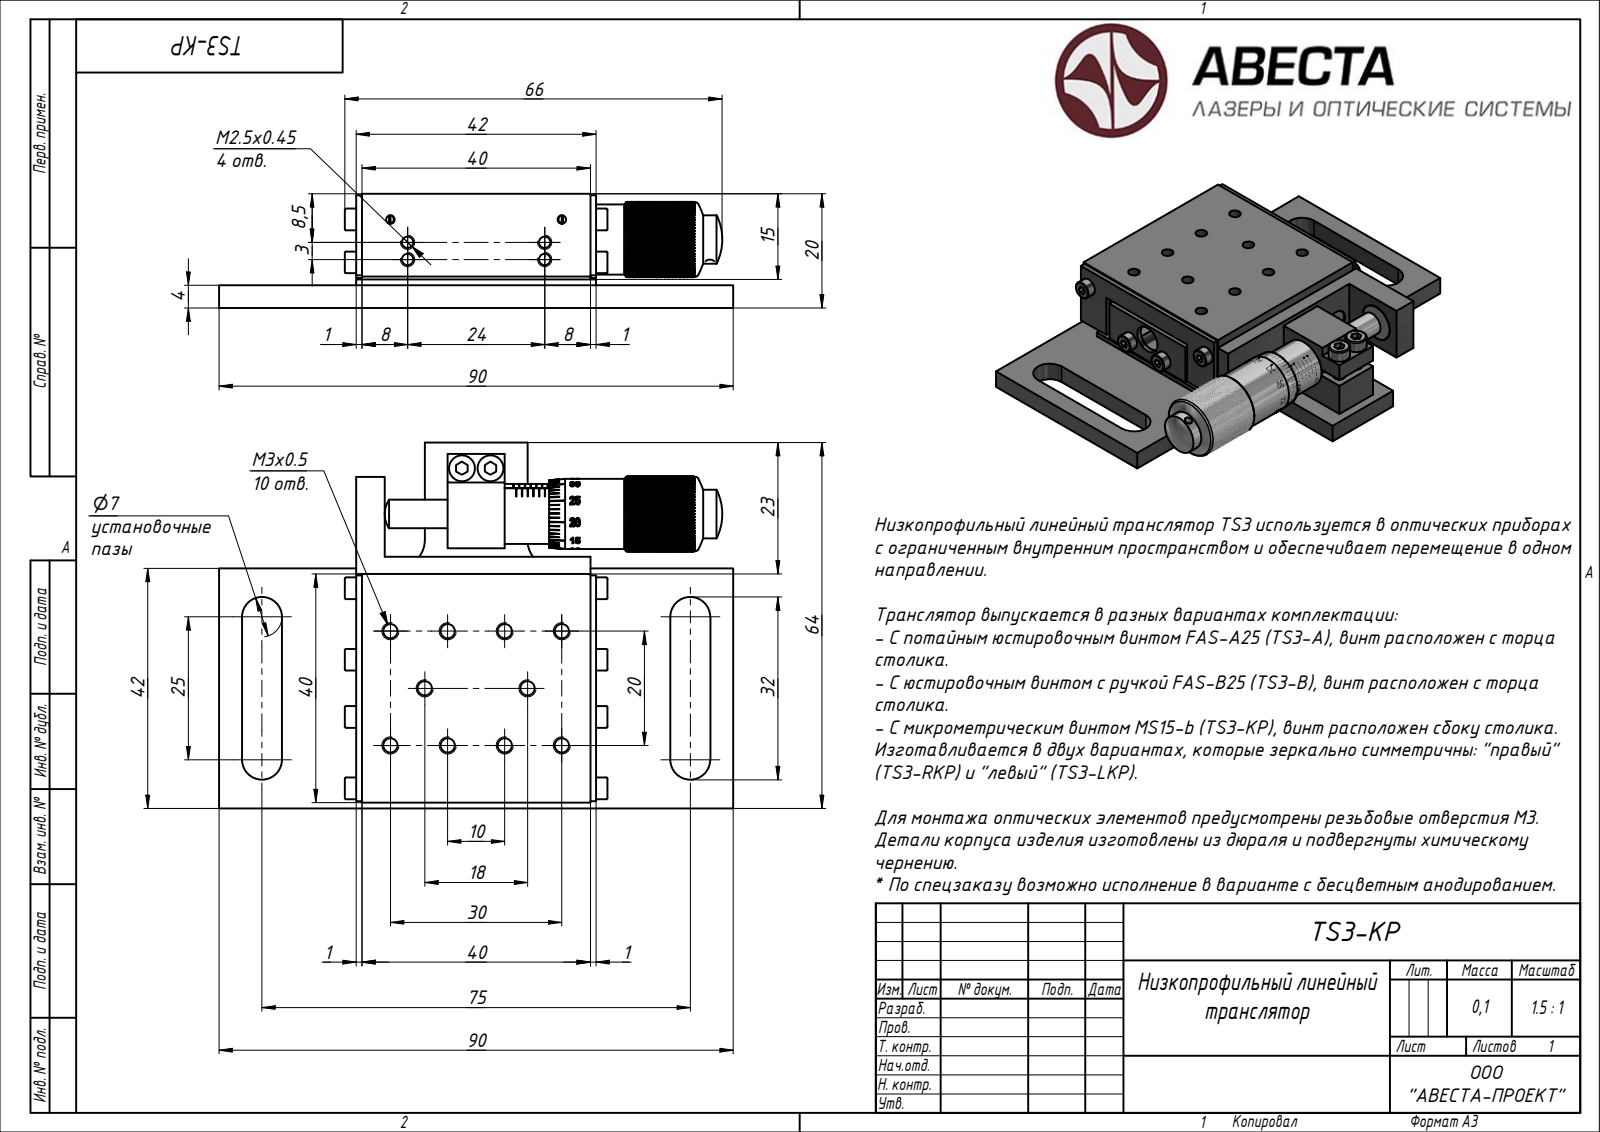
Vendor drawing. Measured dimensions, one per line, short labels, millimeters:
written by: Rhino 7.34 (AUTOMOTIVE_DESIGN)
unit: mm
bodies: 2802 solids, 16801 faces (16191 planar, 280 cylindrical, 330 other)
size: 90 × 64 × 20
volume: 43 985 mm³; area: 28 531 mm²
holes: 14× ⌀2.46, 5× ⌀1.5, 4× ⌀2.5, 4× ⌀2.85, 4× ⌀6.5, 3× ⌀3.5, 3× ⌀5.5, 2× ⌀2.01, 2× ⌀2.46, 2× ⌀3, 1× ⌀1.57, 1× ⌀1.57
bosses: 6× ⌀5.35, 6× ⌀3, 4× ⌀4.5, 4× ⌀3.8, 2× ⌀2.5, 2× ⌀2, 1× ⌀13, 1× ⌀12.3
rounds: 4× R2, 4× R3, 4× R3.5, 2× R1.1, 2× R5, 1× R0.78, 1× R1, 1× R5.25
face distances: 4, 1.5, 7, 20, 16, 1, 5, 2, 11, 15
hole spacings: 10, 5.83, 20, 22.36, 26, 24, 1.5, 3
